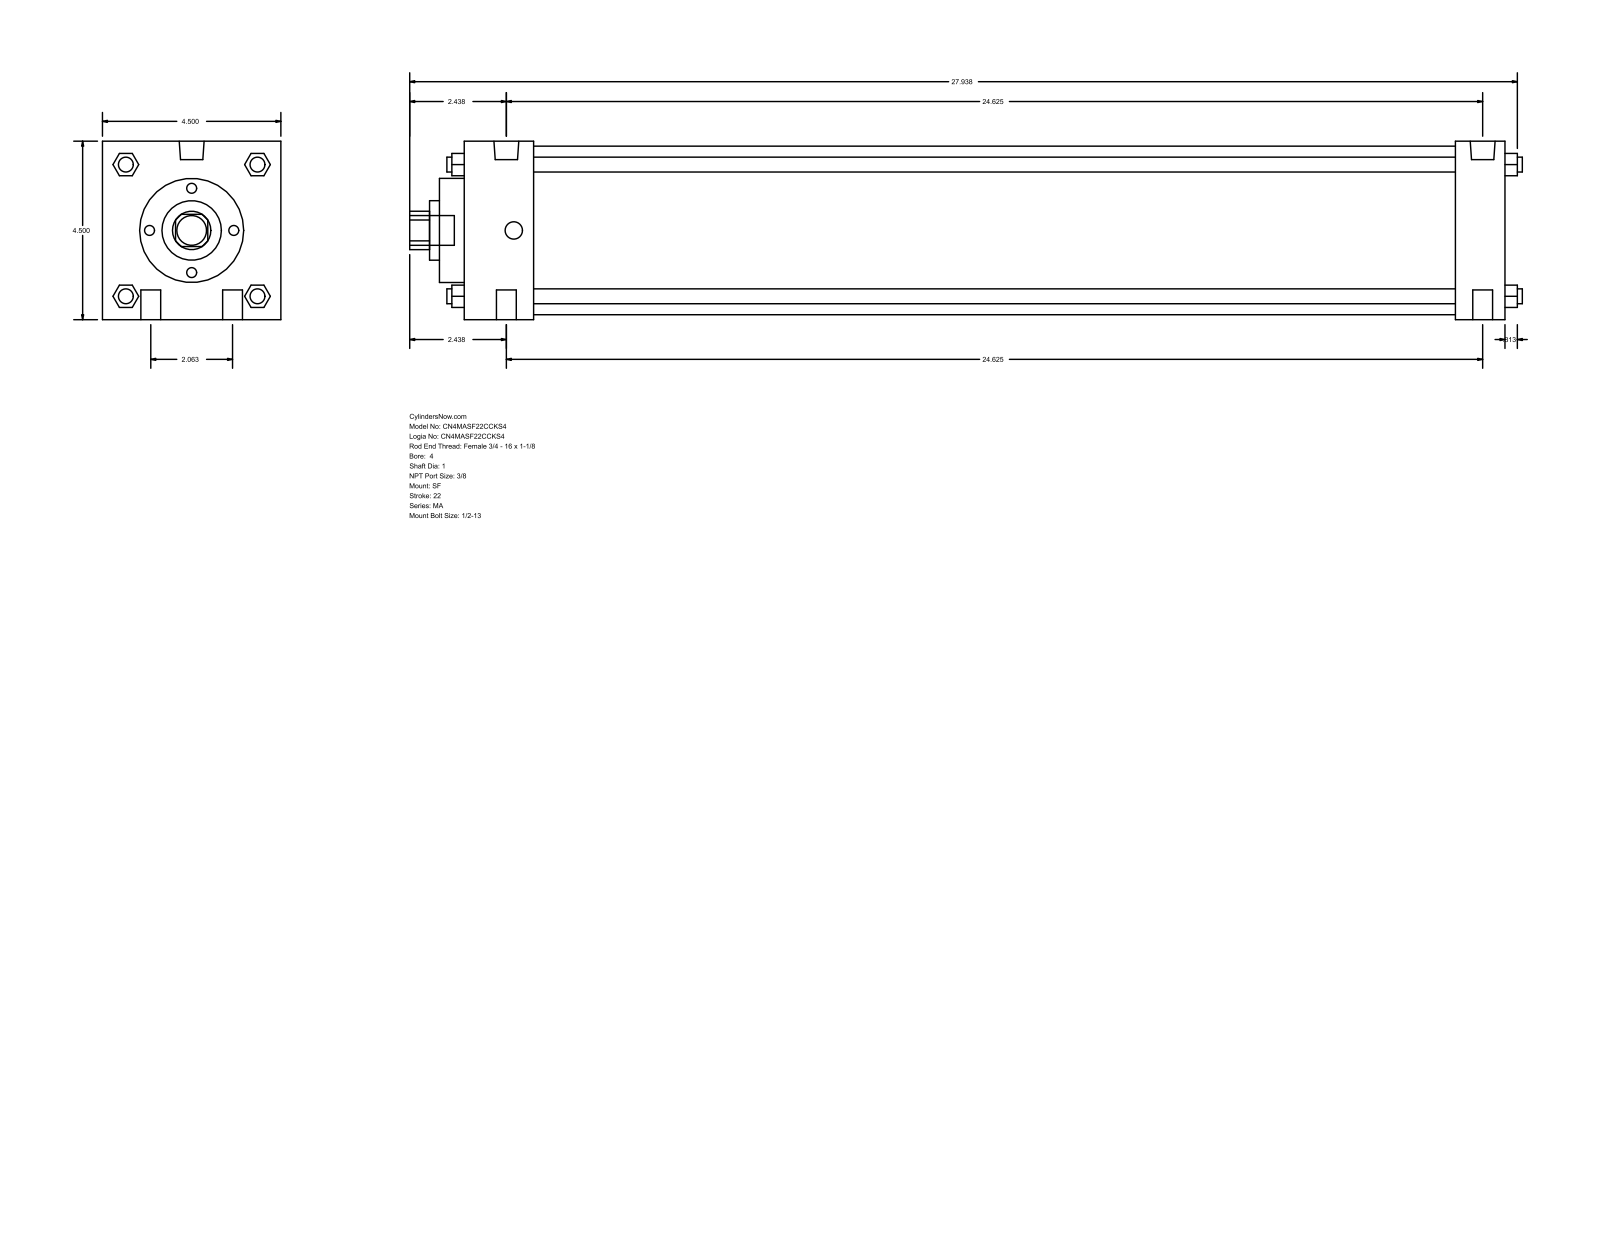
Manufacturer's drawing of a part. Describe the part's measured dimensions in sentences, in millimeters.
The part is named "MA_SF__0400_1". Its 3-D file was written by "GSSL Pune (CONFIG_CONTROL_DESIGN)". It is 0 solids with 126 faces: 95 planar, 31 cylindrical and 0 other. Overall it measures 712.79 by 114.3 by 114.3 millimeters. Round holes: 1 of diameter 25.4, 1 of diameter 38.1, 1 of diameter 66.67, 1 of diameter 107.95. Round bosses or shafts: 4 of diameter 12.7, 4 of diameter 9.53, 2 of diameter 15.93, 2 of diameter 11.11, 1 of diameter 19.05. Partial cylindrical surfaces (rounded edges, fillets, slot ends): 1 of radius 12.29. The main face-to-face distances are 114.3, 666.75, 635, 31.75, 44.46, 590.54, 622.29, 682.62, 15.87, 60.33.
